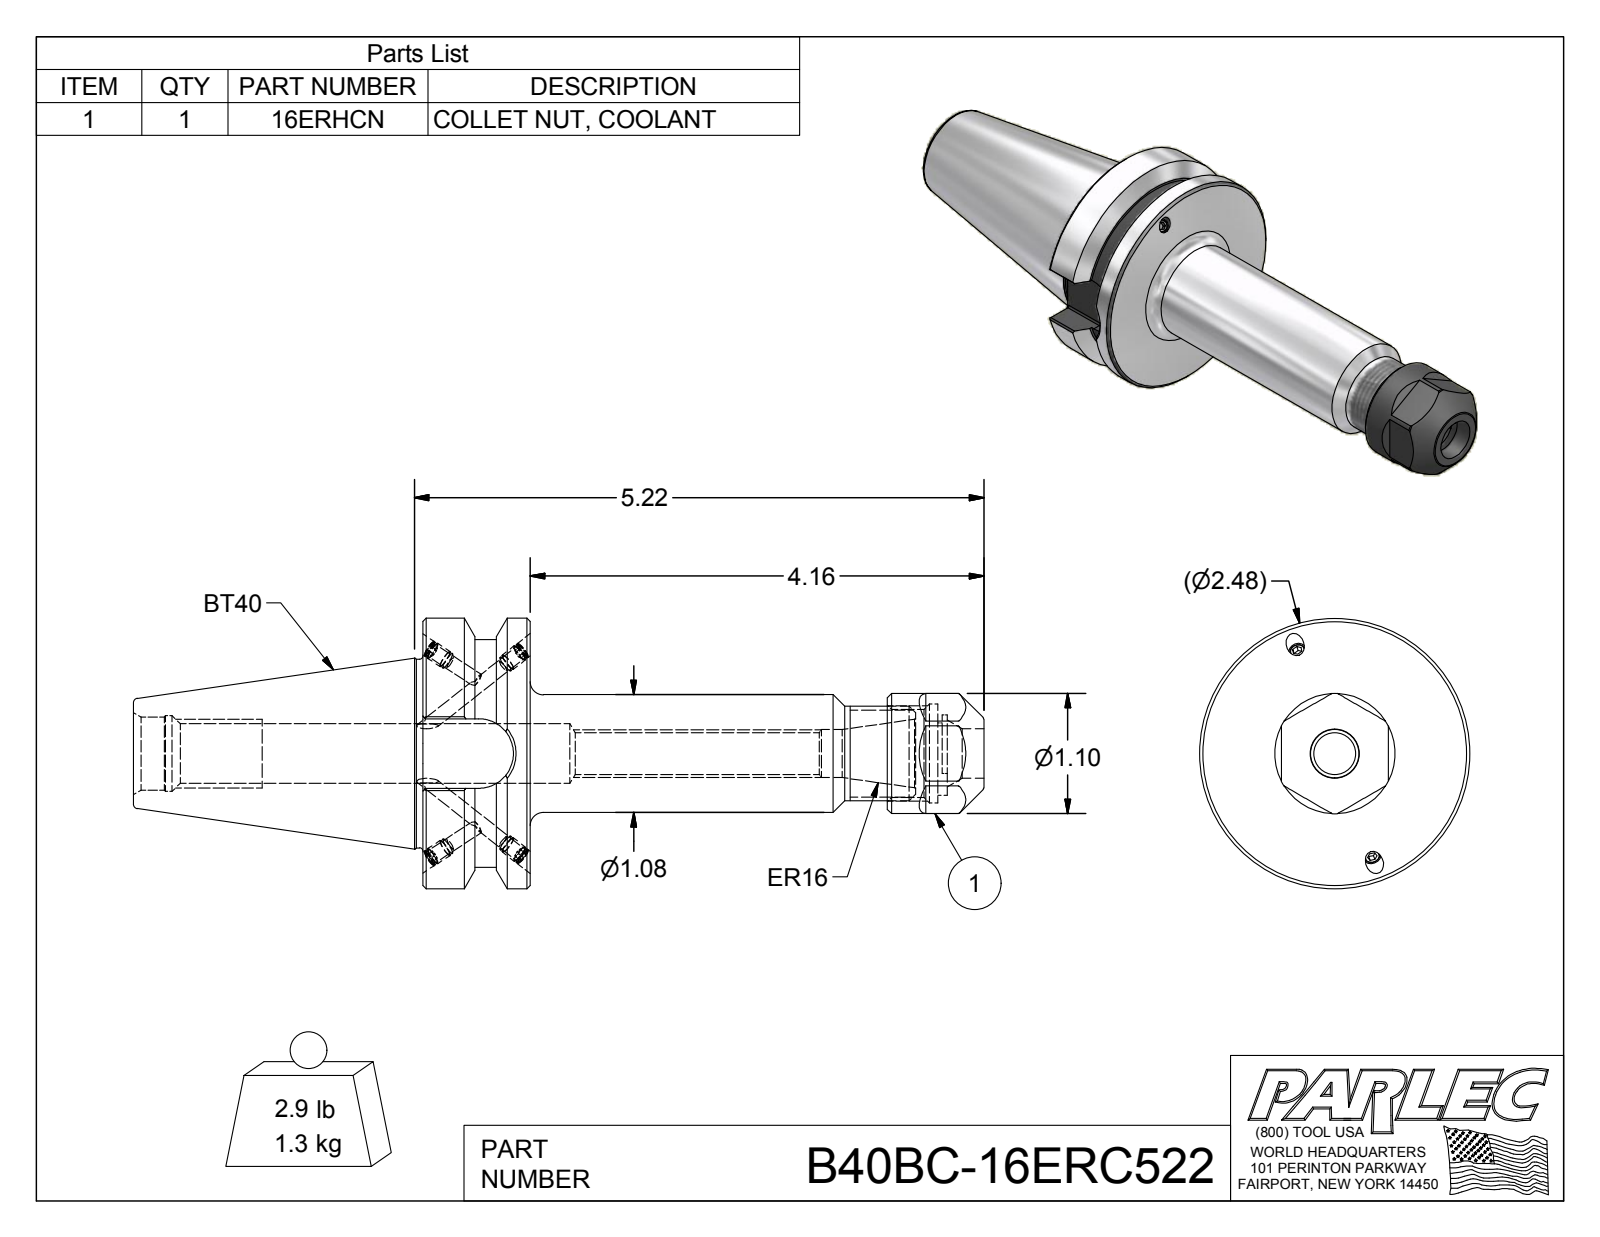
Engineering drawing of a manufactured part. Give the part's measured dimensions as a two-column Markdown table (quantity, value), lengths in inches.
| quantity | value |
| --- | --- |
| part name | B40BC-16ERC522; B40BCB-16ER5-1; 029-965; 16ERHCN |
| STEP written by | Autodesk Inventor 2012 (AUTOMOTIVE_DESIGN) |
| units | inches |
| bodies | 6 solids, 186 faces (84 planar, 49 cylindrical, 53 other) |
| overall size | 7.795 × 2.48 × 2.48 |
| volume | 10.1 in³ |
| surface area | 58.56 in² |
| round holes (diameter × count) | 0.13 × 4, 0.161 × 4, 0.383 × 1, 0.44 × 1, 0.453 × 1, 0.545 × 1, 0.661 × 1, 0.67 × 1, 0.694 × 1, 0.807 × 1, 0.906 × 1 |
| round bosses / shafts (diameter × count) | 0.165 × 4, 0.157 × 4, 2.48 × 1, 2.087 × 1, 1.73 × 1, 1.102 × 1, 1.08 × 1, 0.866 × 1 |
| partial cylindrical surfaces (radius × count) | 0.02 × 8, 0.319 × 1, 0.354 × 1 |
| main face-to-face distances | 0.984, 0.979, 1.78, 0.401, 1.38, 4.721, 3.737, 2.653, 3.637, 7.374 |
| hole center spacings | 0.051 |
